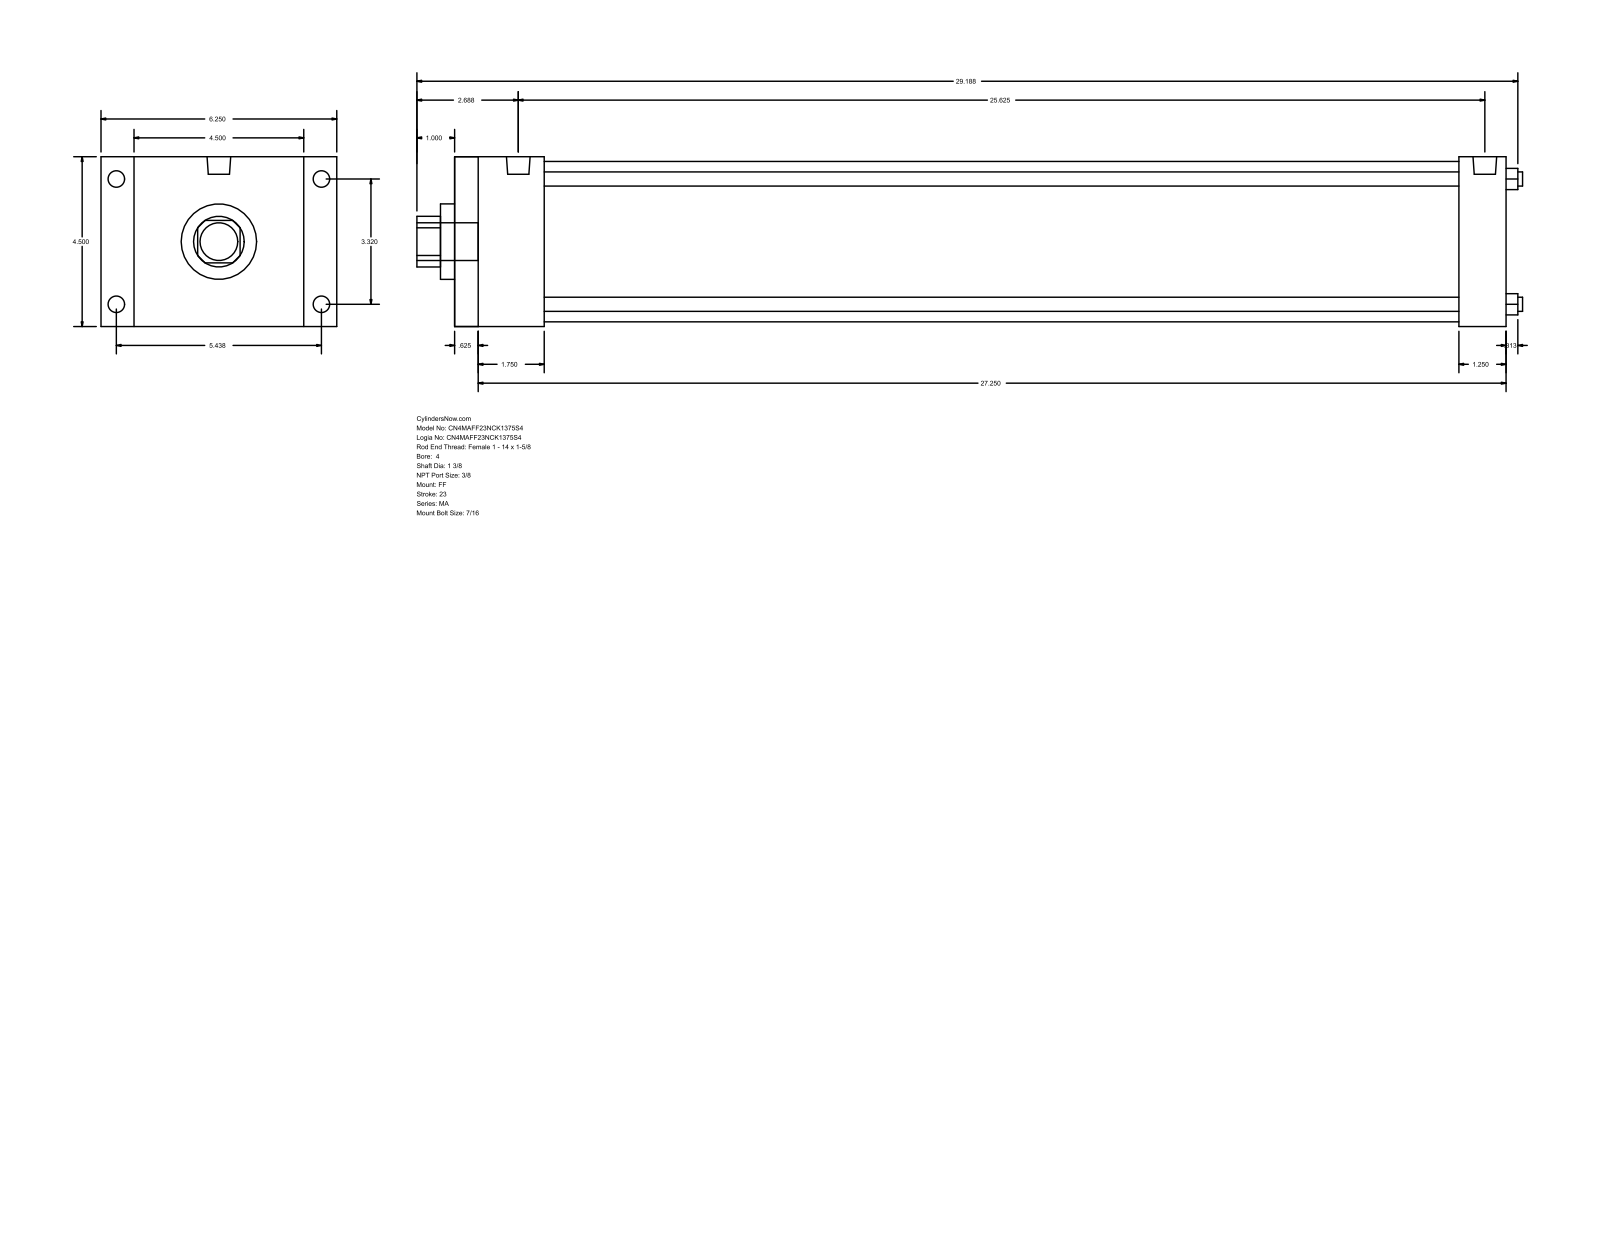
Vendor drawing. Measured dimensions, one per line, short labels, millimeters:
name: MA_FF__0400_1.375
written by: GSSL Pune (CONFIG_CONTROL_DESIGN)
unit: mm
bodies: 0 solids, 92 faces (64 planar, 28 cylindrical, 0 other)
size: 744.54 × 158.75 × 114.3
holes: 4× ⌀9.53, 1× ⌀34.92, 1× ⌀50.8, 1× ⌀107.95
bosses: 8× ⌀11.11, 2× ⌀15.93, 1× ⌀25.4
rounds: 1× R17.06
face distances: 114.3, 708.02, 15.87, 692.15, 22.23, 136.53, 676.27, 660.4, 31.75, 60.32
hole spacings: 59.62, 84.32, 119.25
